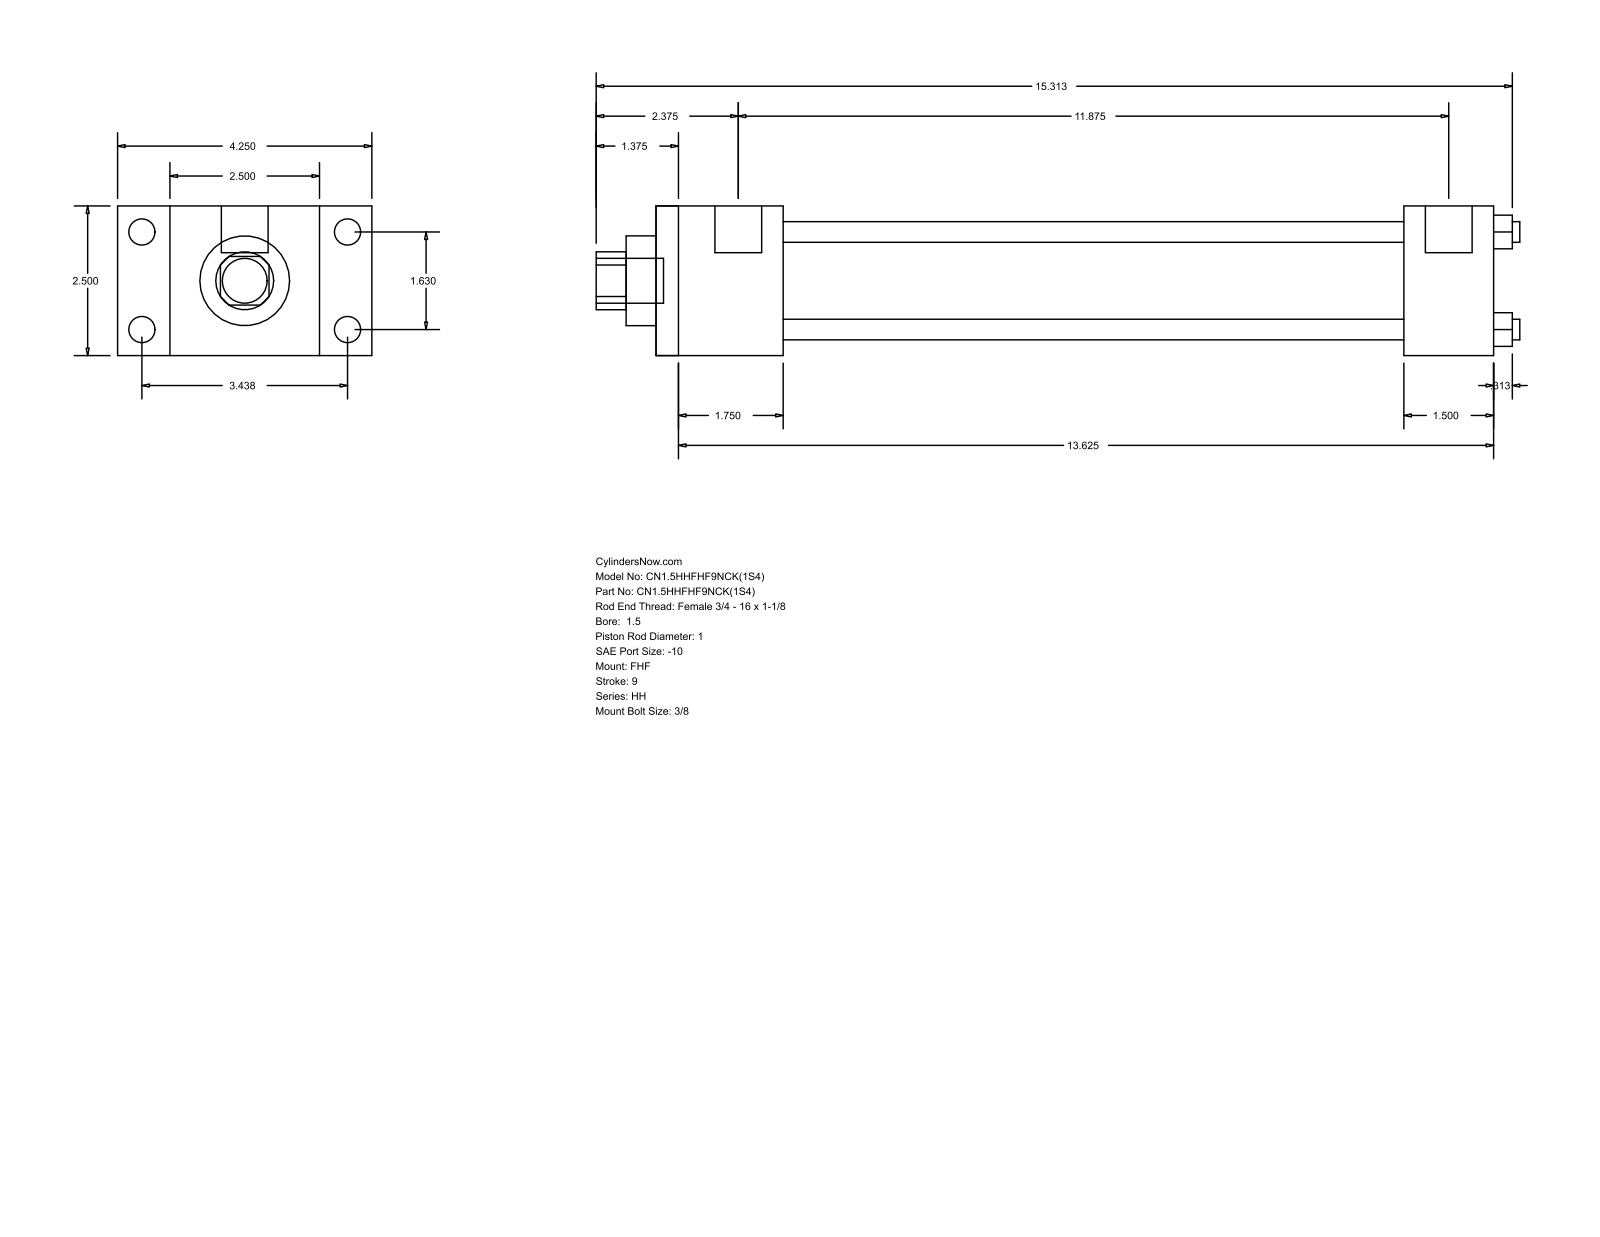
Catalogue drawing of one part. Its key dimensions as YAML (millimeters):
part_name: "HH_FHF__0150_1"
step_written_by: "GSSL Pune (CONFIG_CONTROL_DESIGN)"
units: millimeters
bodies: {solids: 0, faces: 88, planar: 60, cylindrical: 28, other: 0}
overall_size: [392.11, 107.95, 63.5]
round_holes:
  - {diameter: 8.76, count: 4}
  - {diameter: 25.4, count: 1}
  - {diameter: 38.1, count: 1}
  - {diameter: 44.45, count: 1}
round_bosses_or_shafts:
  - {diameter: 11.13, count: 4}
  - {diameter: 5.56, count: 4}
  - {diameter: 19.84, count: 2}
  - {diameter: 19.05, count: 1}
partial_cylinders:
  - {radius: 12.29, count: 1}
face_to_face_distances: [63.5, 22.23, 85.73, 53.98, 107.96, 355.6, 301.62, 317.5, 263.52, 38.1]
hole_center_spacings: [29.27, 41.4, 58.55]
